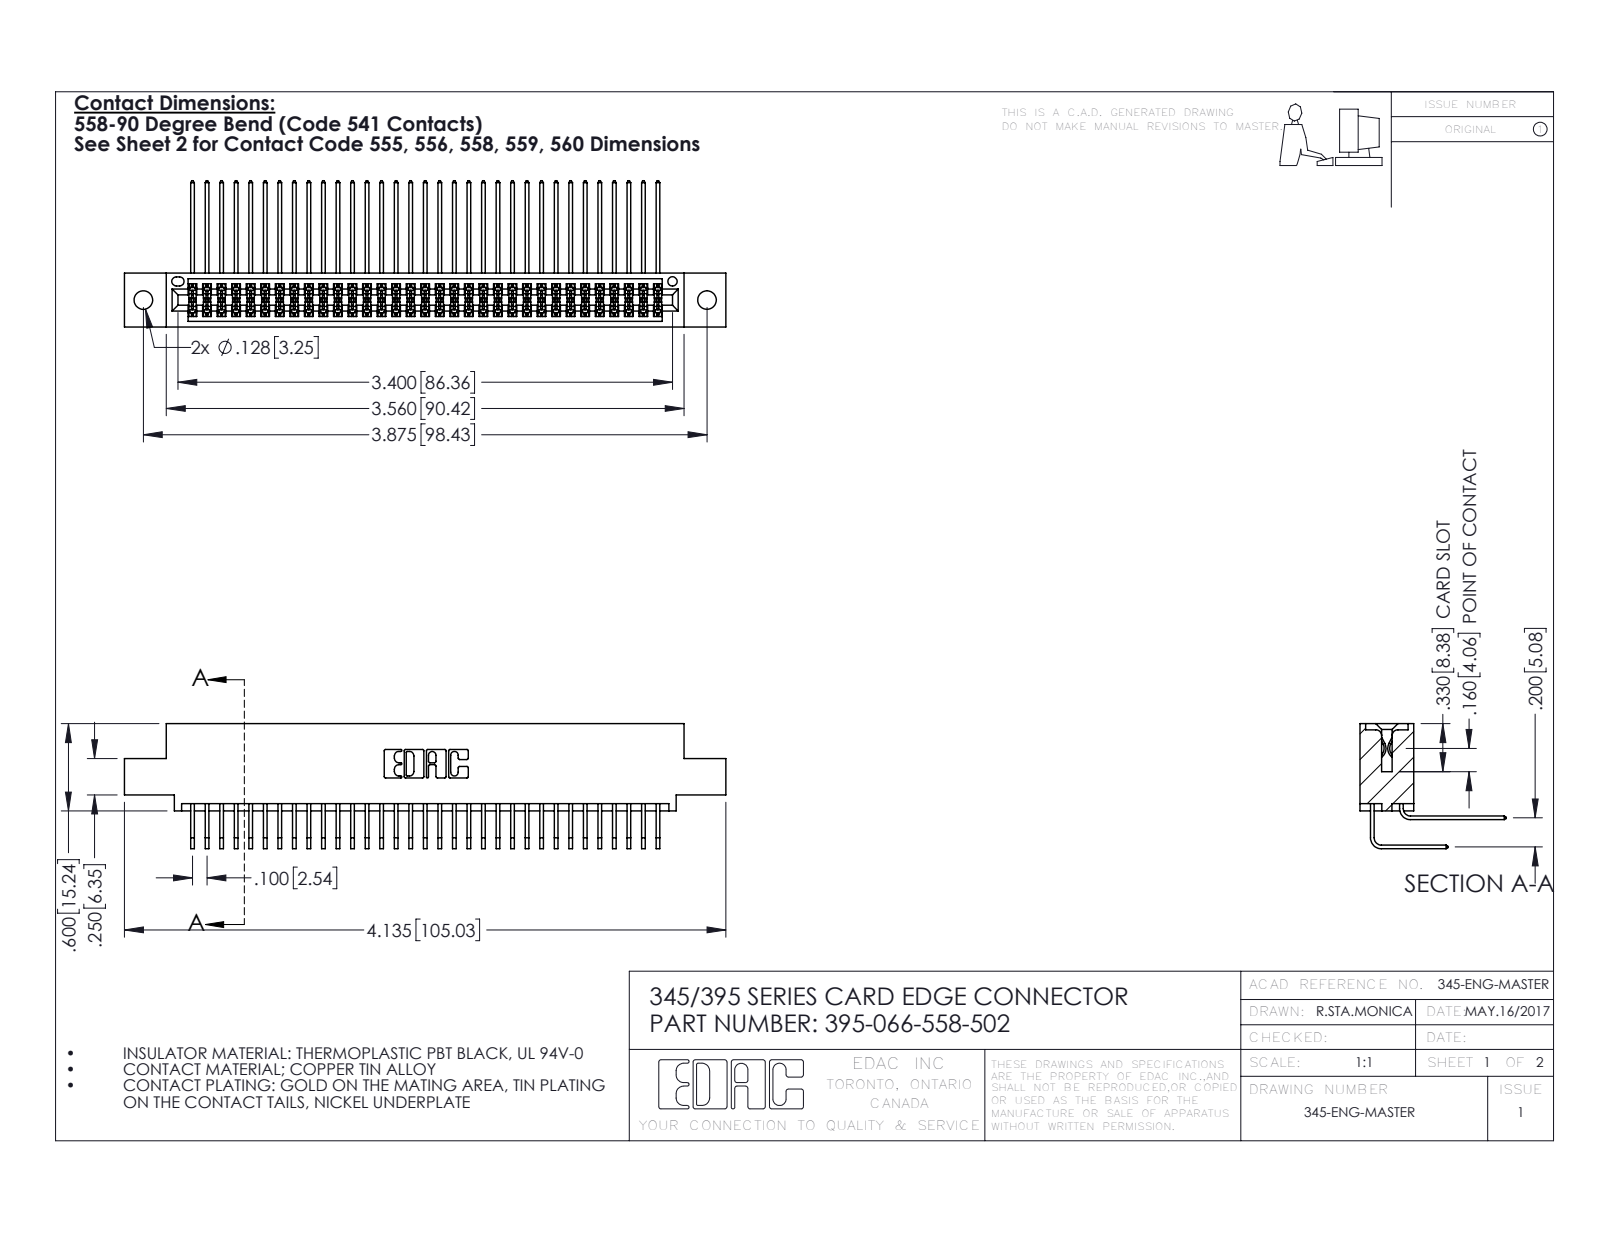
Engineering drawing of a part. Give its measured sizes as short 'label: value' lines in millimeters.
name: 345-292-001_558 Tail - 2; 395-066-558-502; 345-292-001_558 559 Tail - 1; 345 Part_0.110 Offset - 0.128 Dia
written by: SolidWorks 2016 (CONFIG_CONTROL_DESIGN)
unit: mm
bodies: 67 solids, 3562 faces (2394 planar, 1168 cylindrical, 0 other)
size: 105 × 25.5 × 21.8
volume: 10 400 mm³; area: 16 790 mm²
holes: 2× ⌀3.3, 1× ⌀1.6
rounds: 100× R0.2, 22× R0.3, 6× R0.2, 6× R0.8, 3× R0.7, 2× R0.4, 2× R0.5, 2× R0.6
face distances: 1.8, 7.6, 5.1, 9.4, 2.5, 6.9, 0.6, 5.7, 0.6, 4.4
hole spacings: 6.9, 92.5, 98.4
